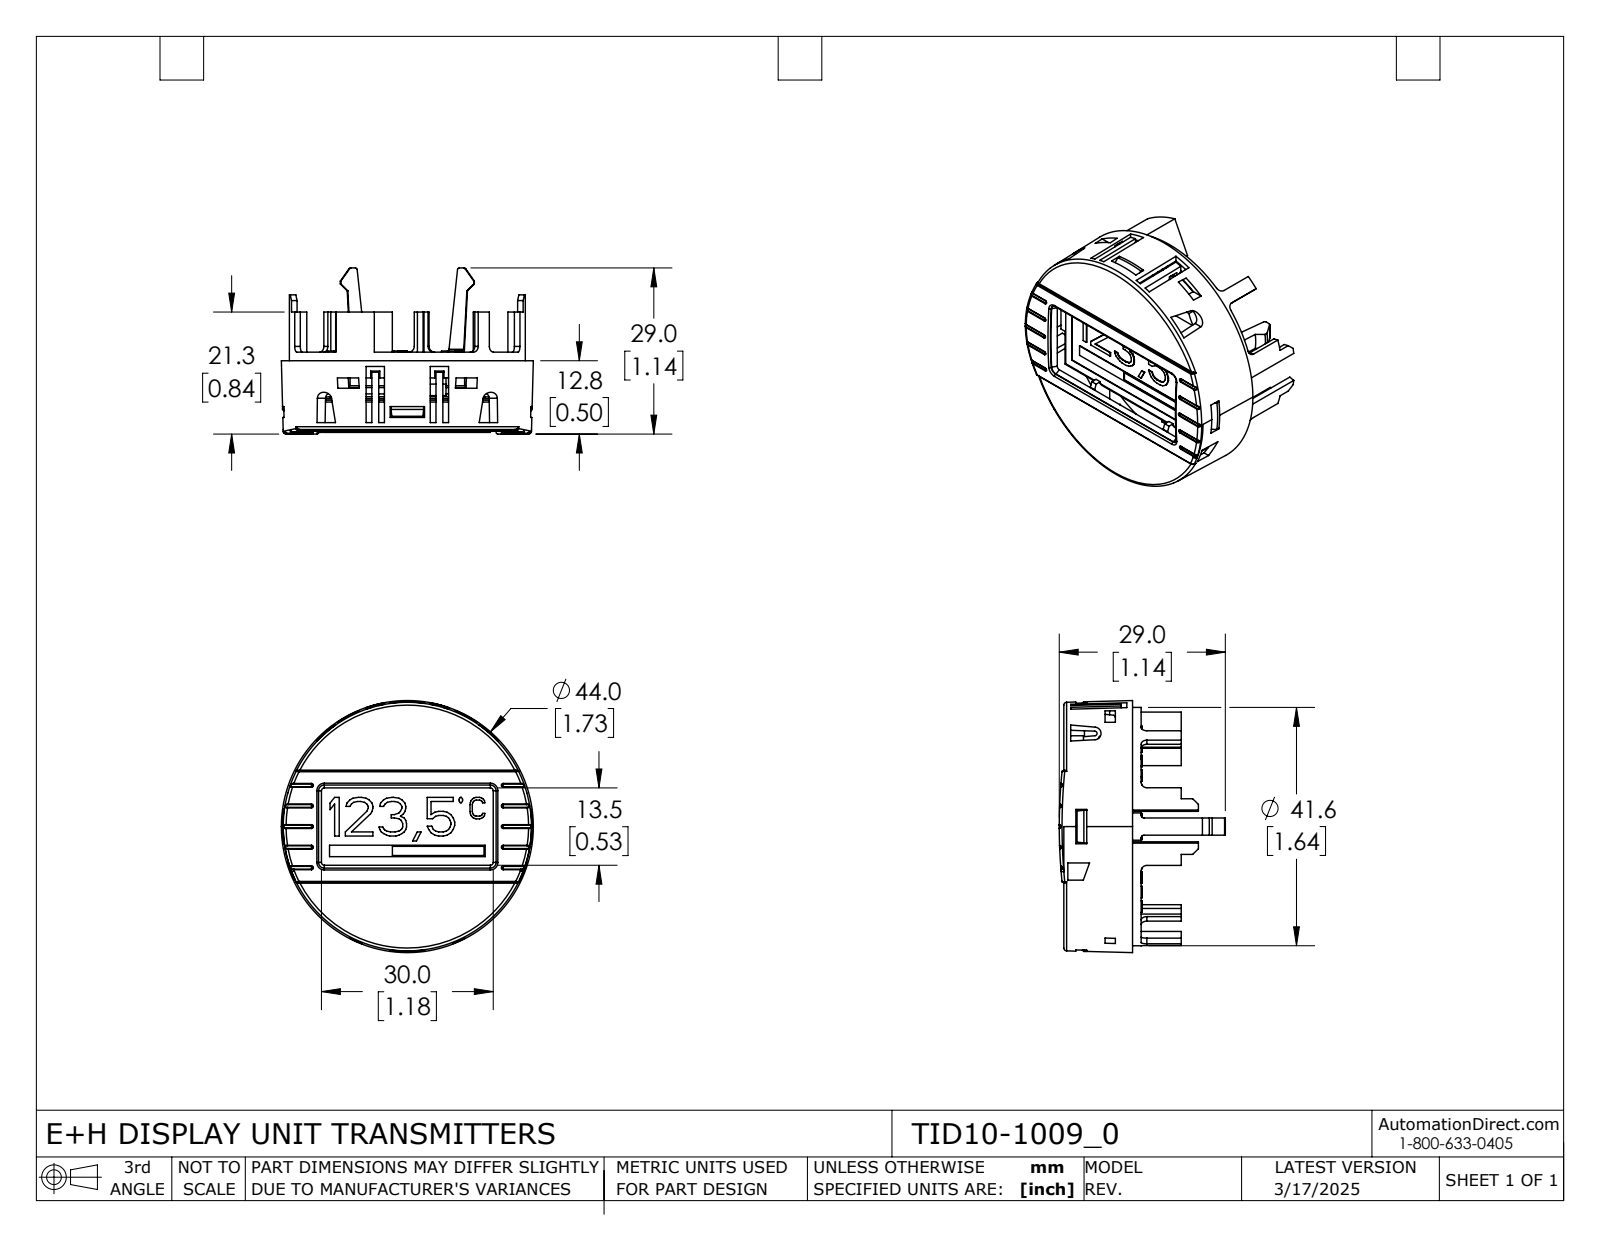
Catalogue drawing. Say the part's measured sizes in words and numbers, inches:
The part is named "TID10-1009_0". Its 3-D file was written by "SolidWorks 2021 (AUTOMOTIVE_DESIGN)". It is 1 solid with 2024 faces: 1803 planar, 116 cylindrical and 105 other. Overall it measures 1.732 by 1.732 by 1.142 inches. Its volume is 0.484 cubic inches and its surface area 20.72 square inches. Round holes: 1 of diameter 1.52. Round bosses or shafts: 1 of diameter 1.638. Partial cylindrical surfaces (rounded edges, fillets, slot ends): 22 of radius 0.039, 12 of radius 0.004, 5 of radius 0.01, 3 of radius 0.02, 2 of radius 0.008, 2 of radius 0.012, 2 of radius 0.047, 2 of radius 0.059. The main face-to-face distances are 0.059, 0.425, 0.047, 0.531, 0.472, 0.484, 0.172, 0.254, 0.231, 0.301.
